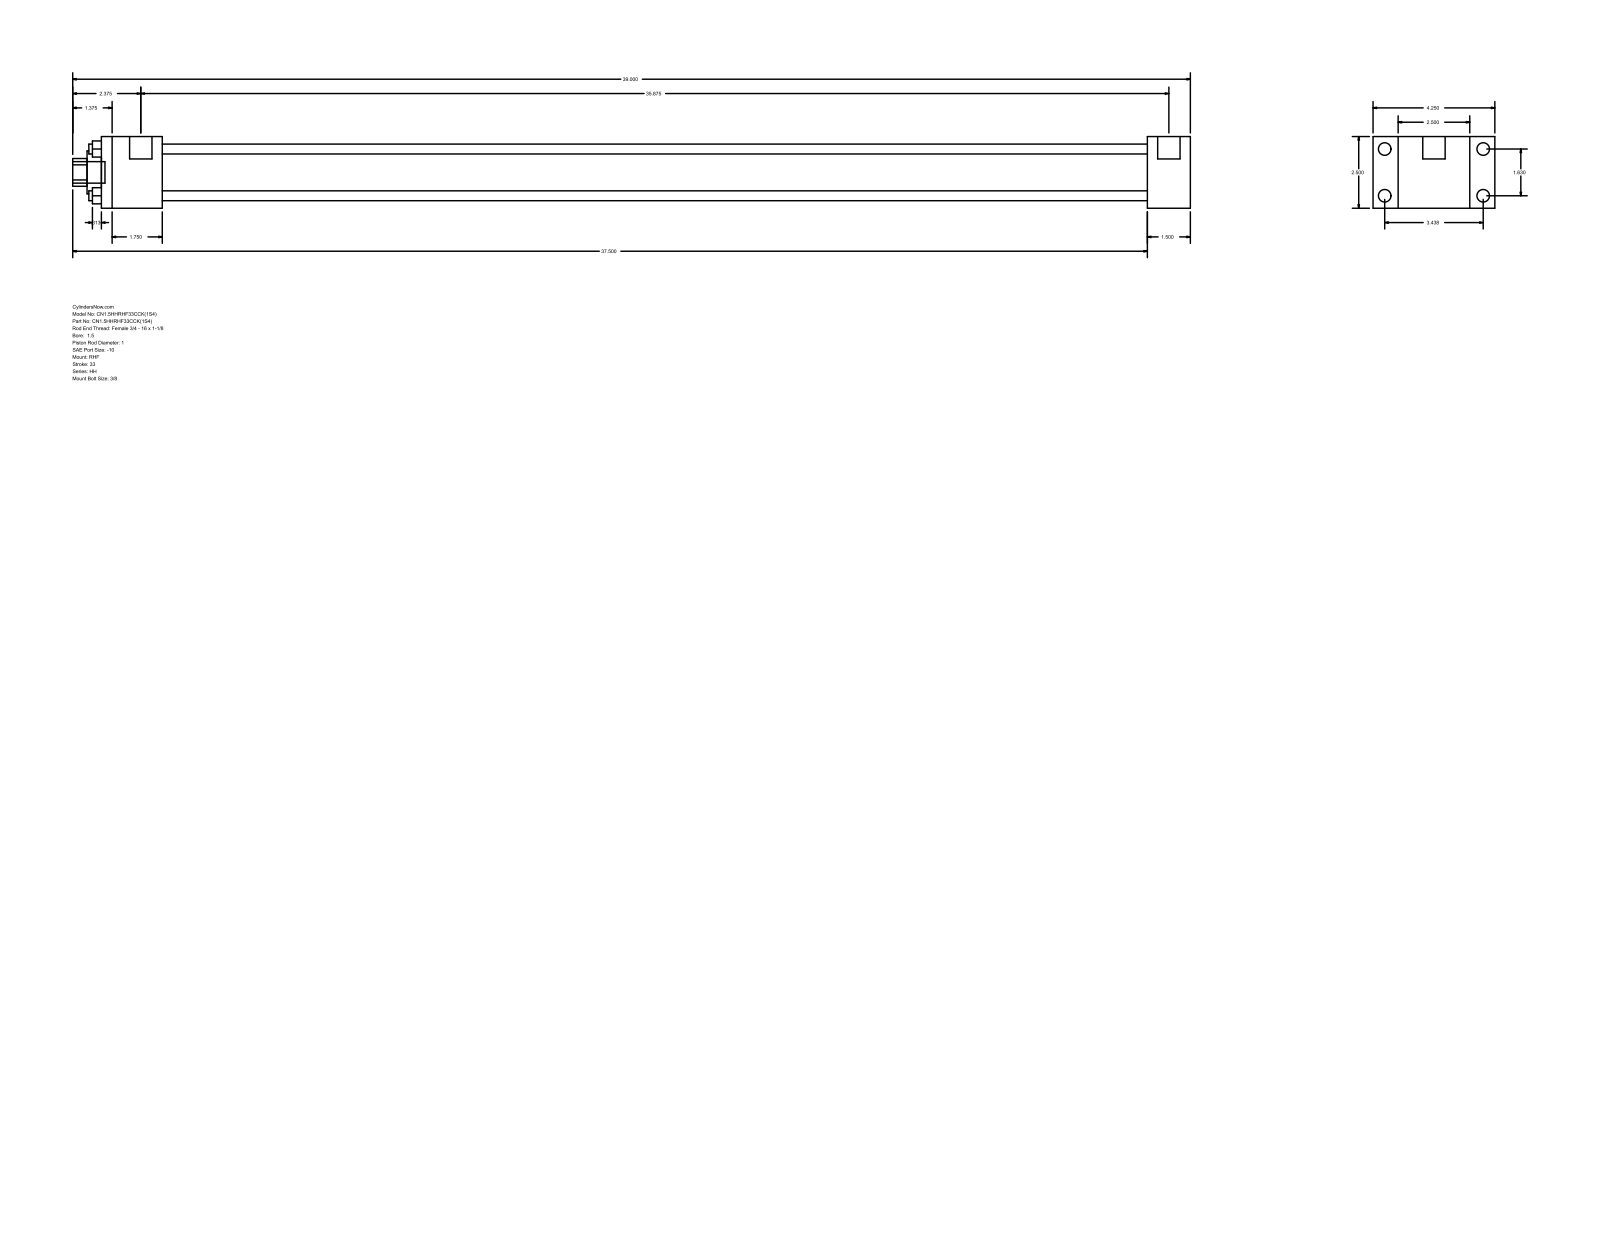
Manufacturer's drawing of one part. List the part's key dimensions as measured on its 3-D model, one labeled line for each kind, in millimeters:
Part name (STEP PRODUCT): HH_RHF__0150_1
STEP written by: GSSL Pune (CONFIG_CONTROL_DESIGN)
Units: millimetres
Bodies: 0 solids, 88 faces (60 planar, 28 cylindrical, 0 other)
Overall size (bounding box): 990.6 × 107.95 × 63.5
Round holes (diameter × count): ⌀8.76 ×4, ⌀25.4 ×1, ⌀38.1 ×1, ⌀44.45 ×1
Round bosses / shafts (diameter × count): ⌀11.13 ×4, ⌀5.56 ×4, ⌀19.84 ×2, ⌀19.05 ×1
Partial cylindrical surfaces — rounded edges, fillets, slot ends (radius × count): R12.29 ×1
Main face-to-face distances: 63.5, 22.23, 85.73, 38.1, 107.96, 873.12, 911.22, 53.98, 927.1, 965.2
Hole centre spacings: 29.27, 41.4, 58.55
